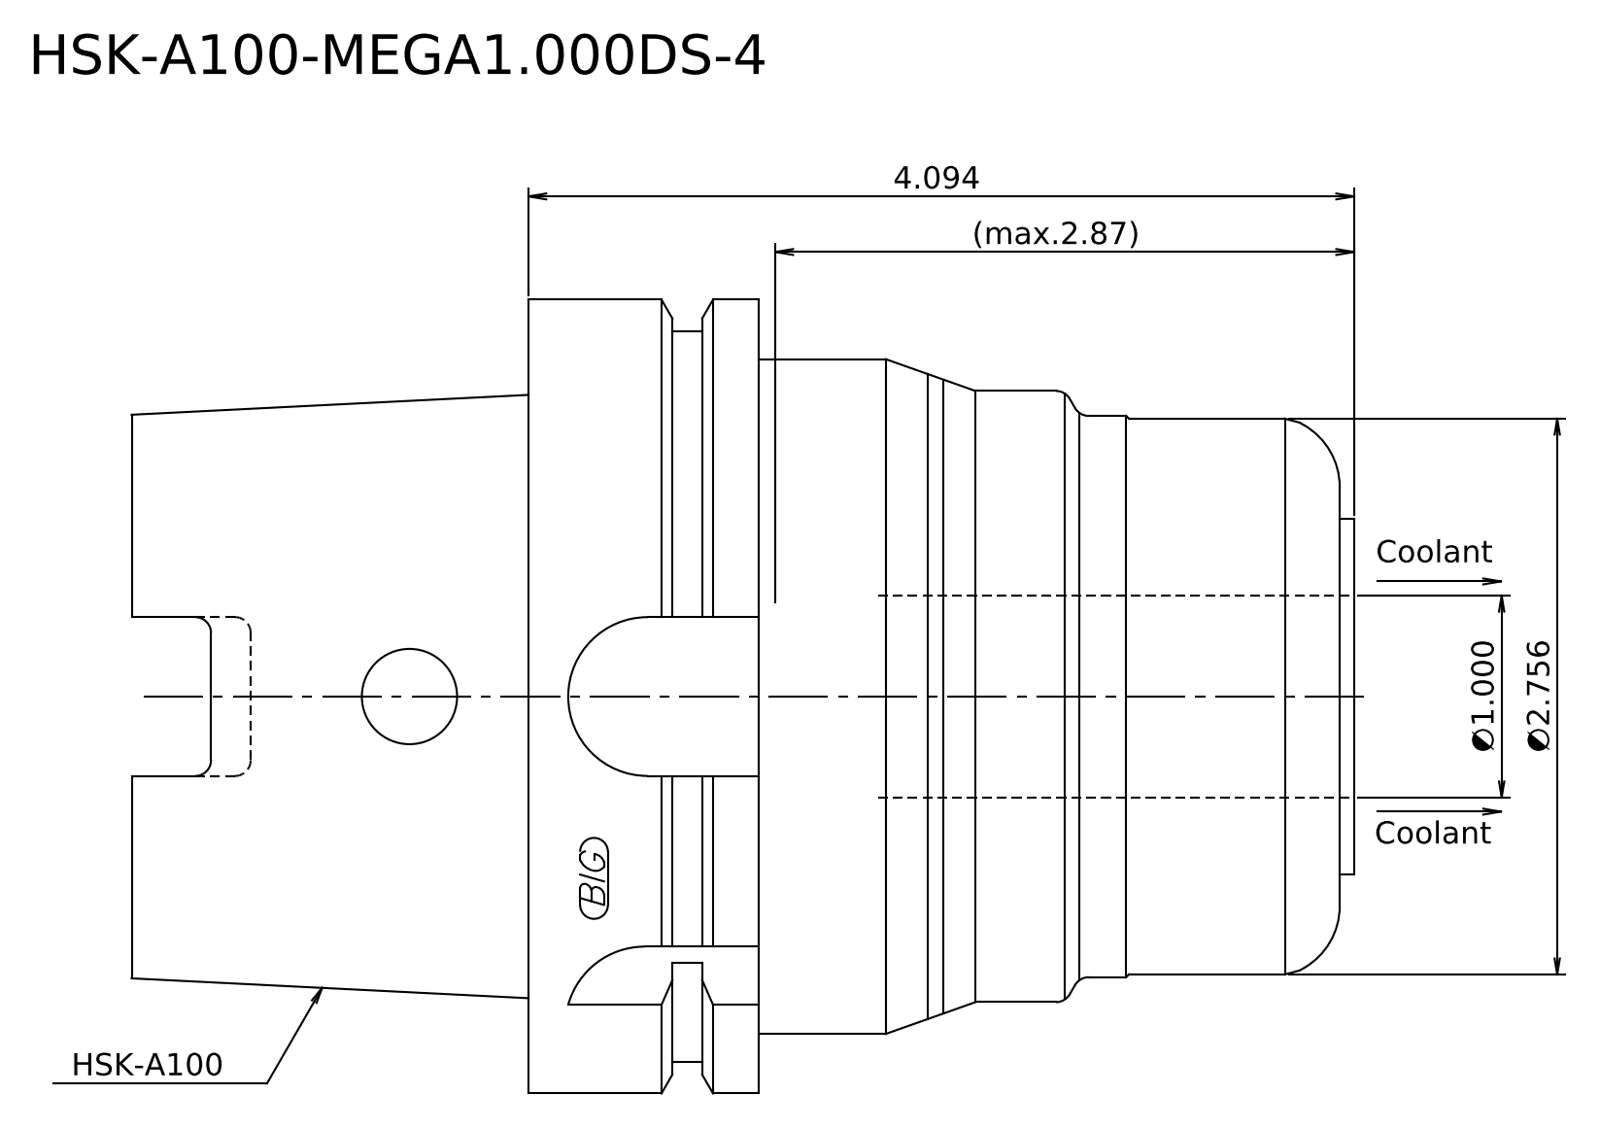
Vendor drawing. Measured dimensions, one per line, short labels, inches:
written by: Kubotek KeyCreator 2011 V10.0.2 (22737) (automotive_design)
unit: in
bodies: 1 solid, 23 faces (7 planar, 8 cylindrical, 8 other)
size: 6.063 × 3.937 × 3.937
volume: 47.05 in³; area: 82.68 in²
bosses: 1× ⌀3.937, 1× ⌀3.622, 1× ⌀3.346, 1× ⌀3.031, 1× ⌀2.783, 1× ⌀2.756, 1× ⌀1.763
face distances: 1.969, 1.142, 3.11, 2.953, 4.094, 6.063, 0.071, 2.882, 4.024, 5.992
